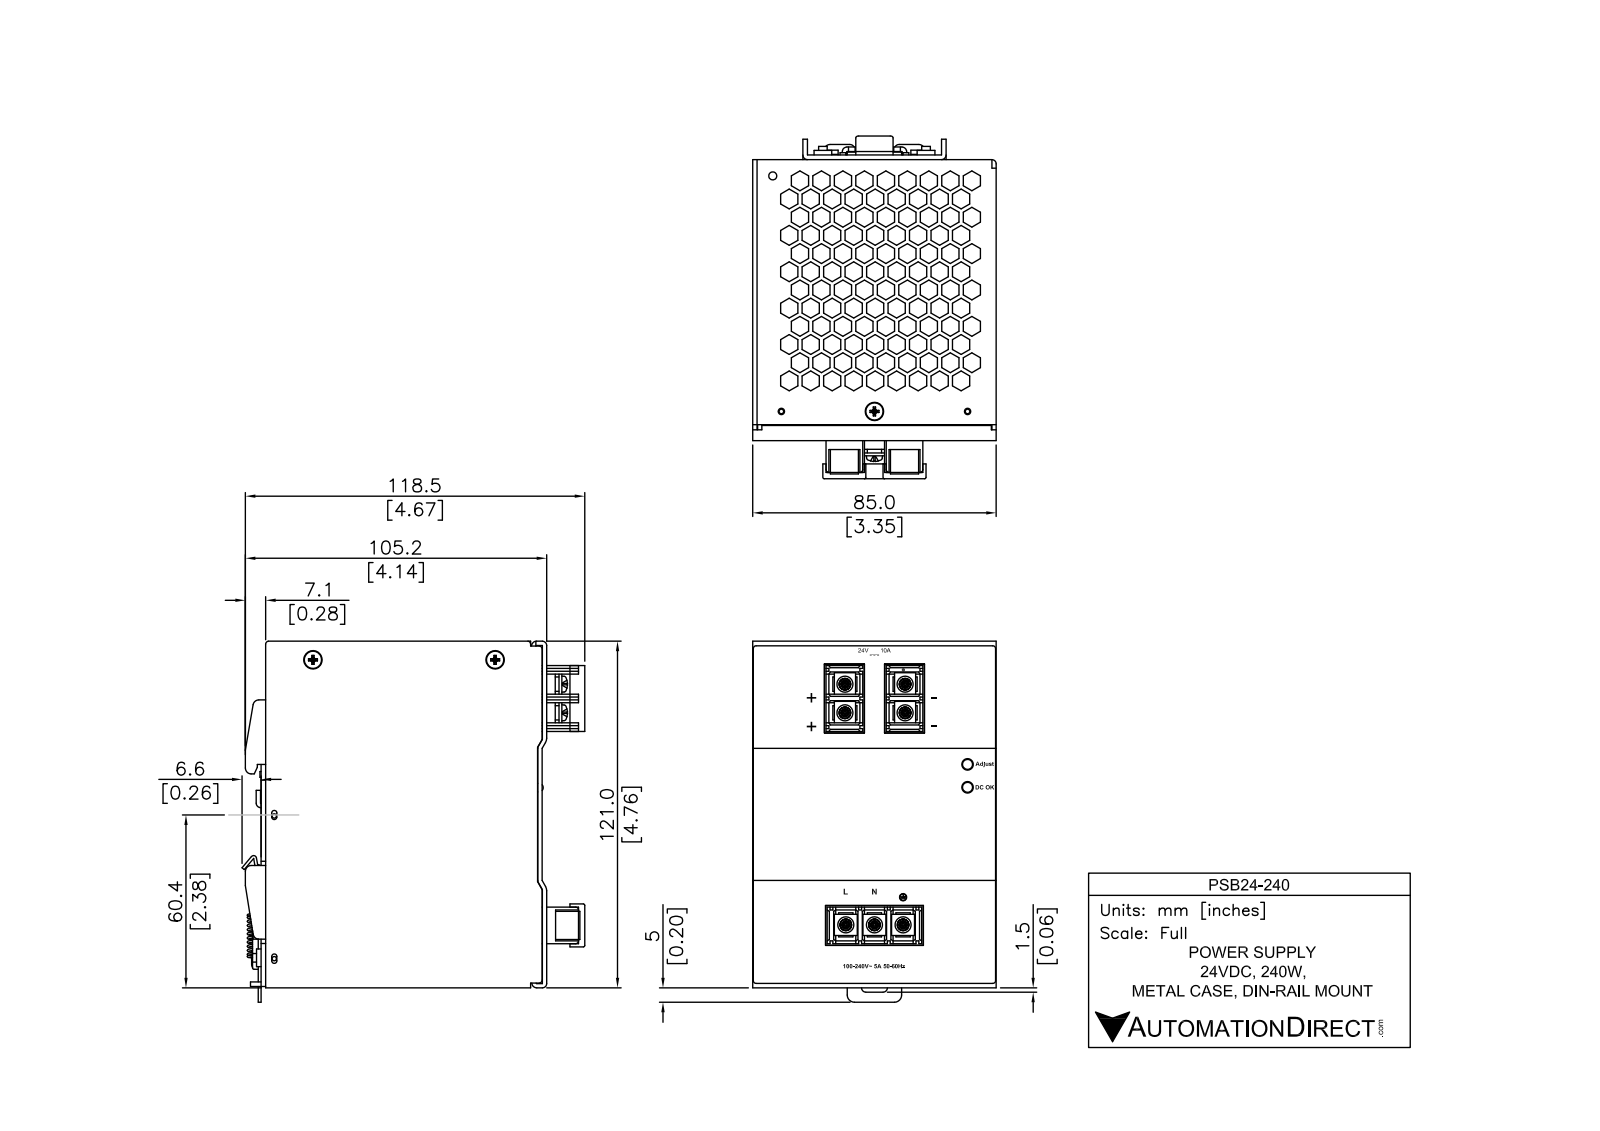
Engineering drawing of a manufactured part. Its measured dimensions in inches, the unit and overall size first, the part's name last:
Units: inches
Overall size (bounding box): 4.946 × 4.612 × 3.35
Round holes (diameter × count): ⌀0.145 ×1, ⌀0.145 ×1
Round bosses / shafts (diameter × count): ⌀0.23 ×4, ⌀0.125 ×4, ⌀0.205 ×3
Partial cylindrical surfaces — rounded edges, fillets, slot ends (radius × count): R0.06 ×22, R0.03 ×13, R0.05 ×8, R0.04 ×2, R0.075 ×2, R0.13 ×2, R0.01 ×1, R0.07 ×1
Main face-to-face distances: 0.163, 3.183, 0.13, 0.293, 3.053, 2.89, 3.346, 3.02, 2.76, 3.652
Hole centre spacings: 0.3
Volume: 54.75 in³ · Surface area: 243.7 in²
Bodies: 1 solid, 1969 faces (1789 planar, 100 cylindrical, 80 other)
Part name (STEP PRODUCT): PSB24-240
STEP written by: SolidWorks 2011 (CONFIG_CONTROL_DESIGN)
